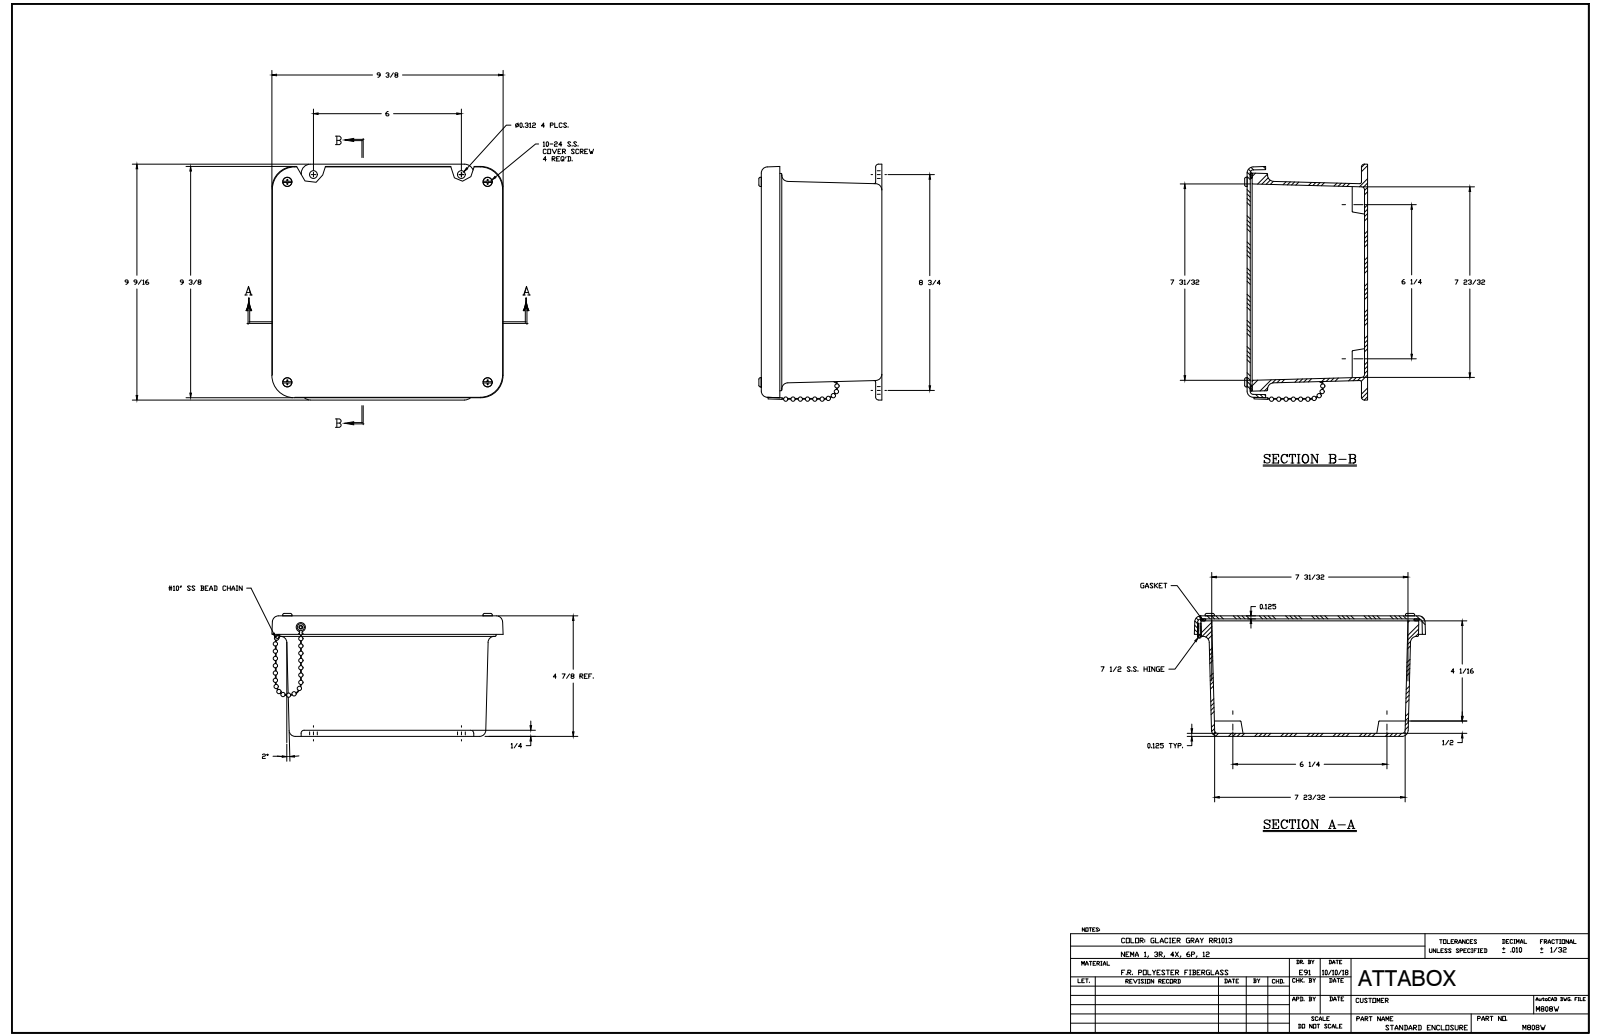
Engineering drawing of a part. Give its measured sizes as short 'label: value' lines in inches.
name: M808W
written by: SolidWorks 2018 (AUTOMOTIVE_DESIGN)
unit: in
bodies: 47 solids, 975 faces (202 planar, 317 cylindrical, 456 other)
size: 10.047 × 9.64 × 5.005
volume: 51.18 in³; area: 717.8 in²
holes: 8× ⌀0.152, 4× ⌀0.14, 4× ⌀0.145, 4× ⌀0.156, 4× ⌀0.218, 2× ⌀0.187, 1× ⌀0.126
bosses: 8× ⌀0.27, 4× ⌀0.19, 4× ⌀0.156, 2× ⌀0.25, 2× ⌀0.125, 1× ⌀0.375, 1× ⌀0.375, 1× ⌀0.283
rounds: 36× R0.031, 12× R0.125, 12× R0.25, 8× R0.2, 4× R0.031, 4× R0.375, 2× R0.01, 2× R0.063
face distances: 0.125, 4.749, 4.874, 4.624, 0.125, 4.749, 0.189, 0.064, 4.685, 4.56
hole spacings: 7.249, 1.326, 6.25, 8.125, 10.165, 8.839, 11.491, 3
